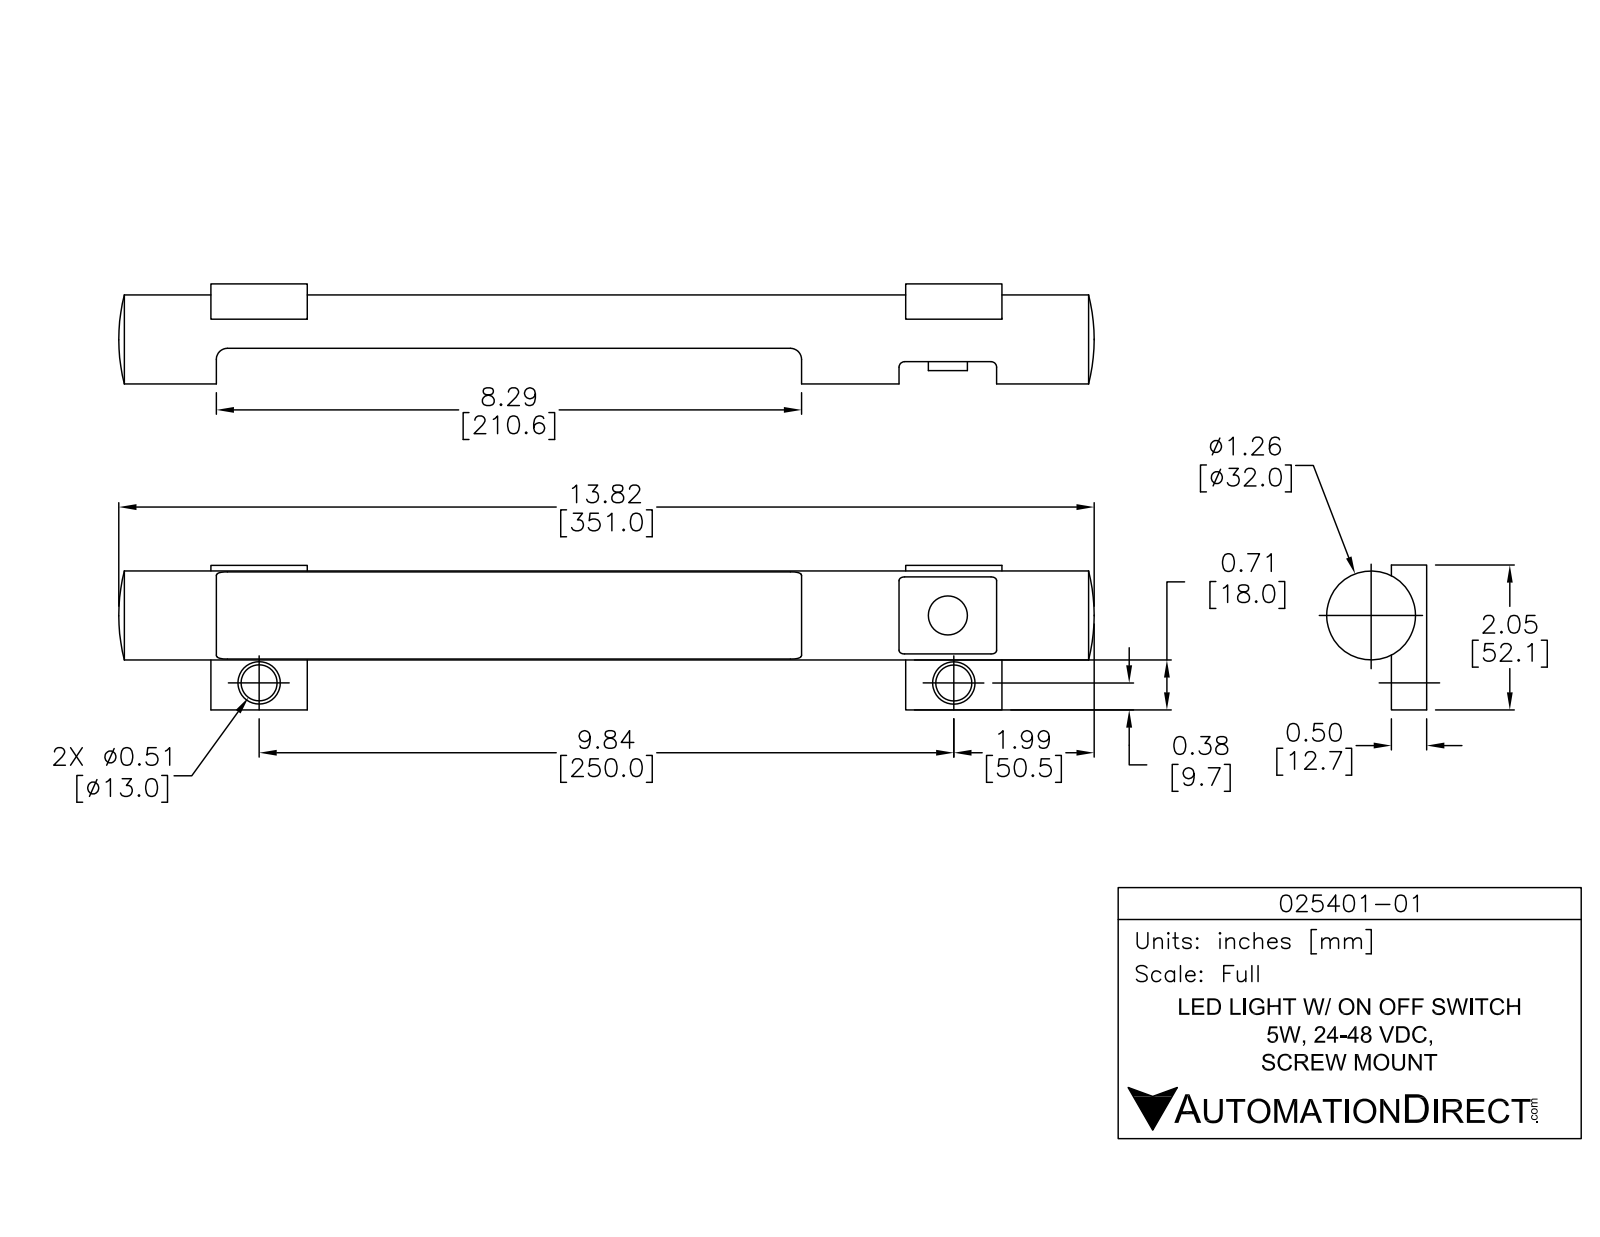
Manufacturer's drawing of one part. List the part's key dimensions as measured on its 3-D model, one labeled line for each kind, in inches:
Part name (STEP PRODUCT): 025401-01
STEP written by: SolidWorks 2013 (AUTOMOTIVE_DESIGN)
Units: inches
Bodies: 1 solid, 176 faces (99 planar, 35 cylindrical, 42 other)
Overall size (bounding box): 13.758 × 2.01 × 1.37
Volume: 14.61 in³ · Surface area: 65.72 in²
Round holes (diameter × count): ⌀0.077 ×2, ⌀0.23 ×2
Round bosses / shafts (diameter × count): ⌀0.073 ×2, ⌀1.26 ×1
Partial cylindrical surfaces — rounded edges, fillets, slot ends (radius × count): R0.06 ×4, R0.103 ×4, R0.2 ×4, R0.12 ×2, R0.629 ×2, R0.03 ×1, R1.209 ×1
Main face-to-face distances: 0.905, 2.01, 0.03, 0.545, 0.22, 0.325, 0.45, 0.1, 0.03, 0.55
Hole centre spacings: 0.2, 9.801
